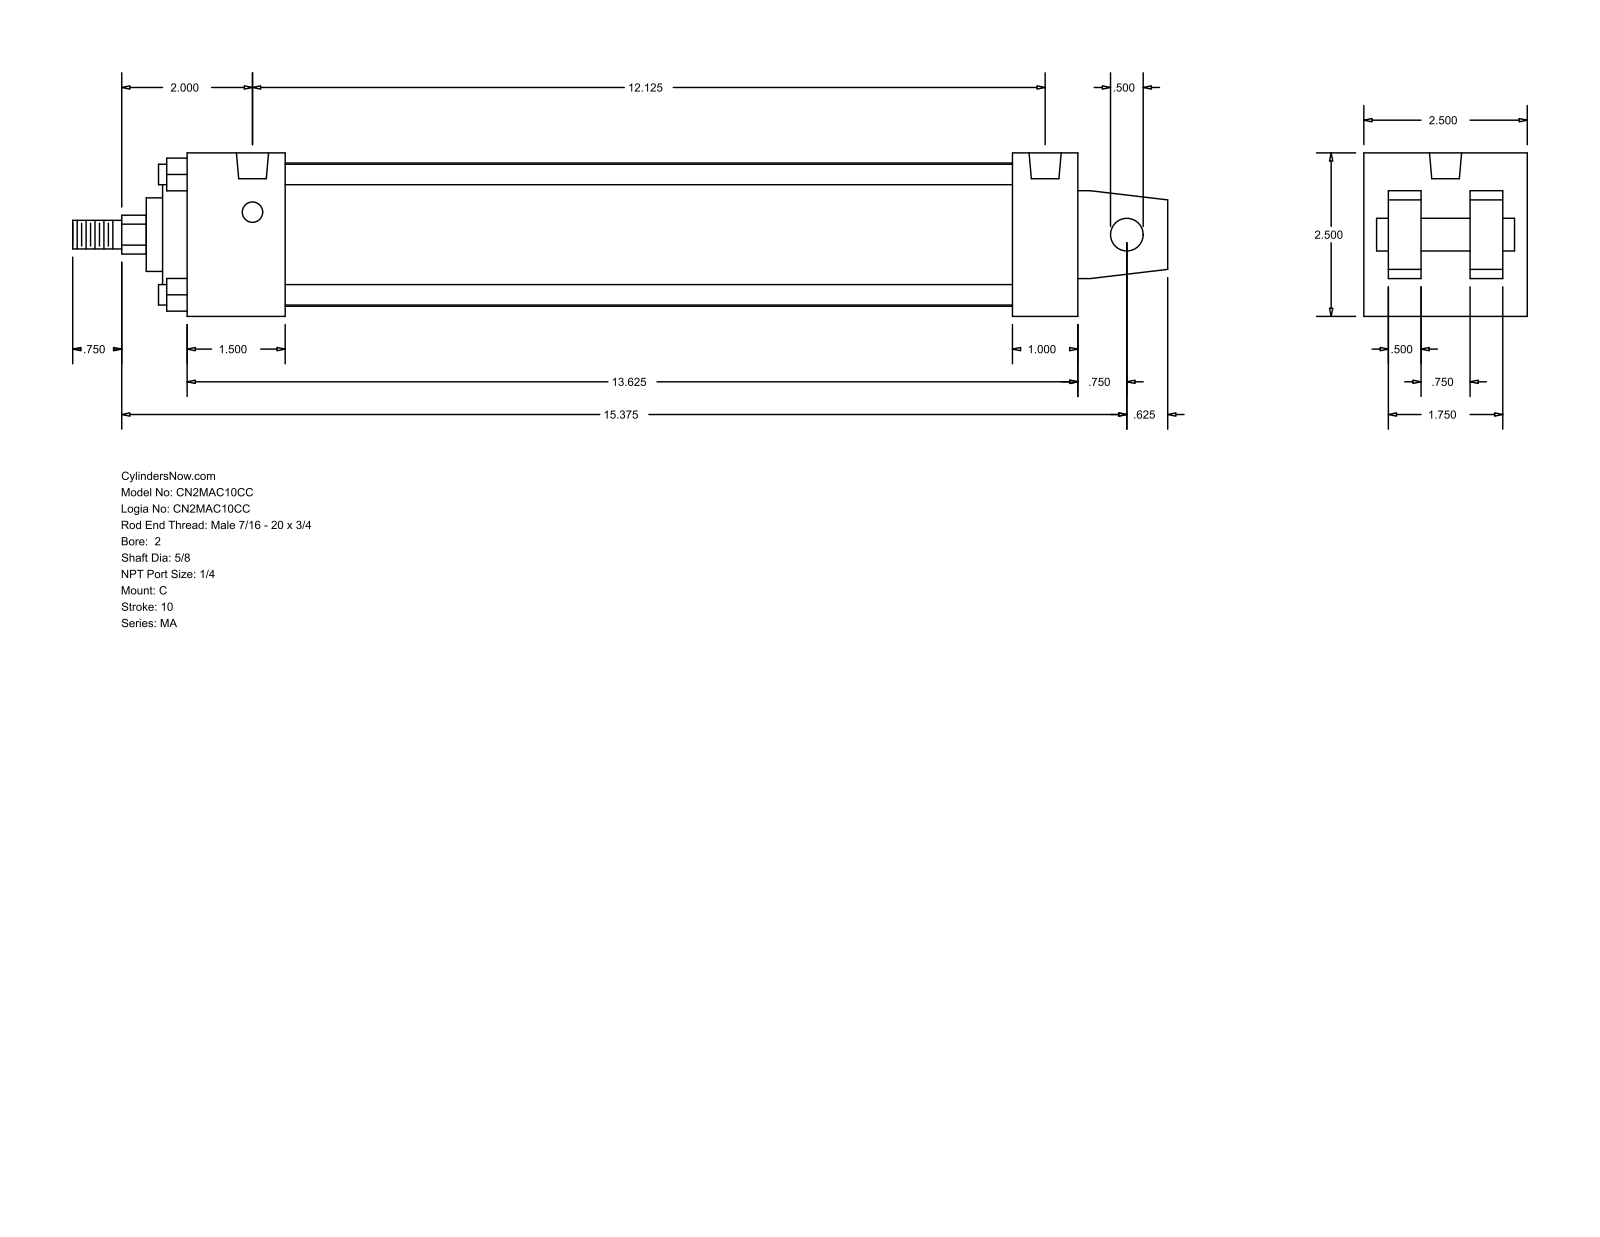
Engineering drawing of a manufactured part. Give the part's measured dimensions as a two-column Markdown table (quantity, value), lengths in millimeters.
| quantity | value |
| --- | --- |
| part name | MA_C__0200_0.625 |
| STEP written by | GSSL Pune (CONFIG_CONTROL_DESIGN) |
| units | millimeters |
| bodies | 0 solids, 105 faces (77 planar, 28 cylindrical, 0 other) |
| overall size | 425.45 × 63.5 × 63.5 |
| round holes (diameter × count) | 7.94 × 4, 12.49 × 2 |
| round bosses / shafts (diameter × count) | 7.94 × 4, 55.63 × 1, 50.8 × 1, 28.57 × 1, 15.88 × 1, 12.7 × 1, 11.11 × 1 |
| partial cylindrical surfaces (radius × count) | 7.54 × 1 |
| main face-to-face distances | 63.5, 9.52, 12.7, 22.22, 41.28, 53.98, 31.76, 38.1, 346.08, 307.98 |
| hole center spacings | 307.97 |
